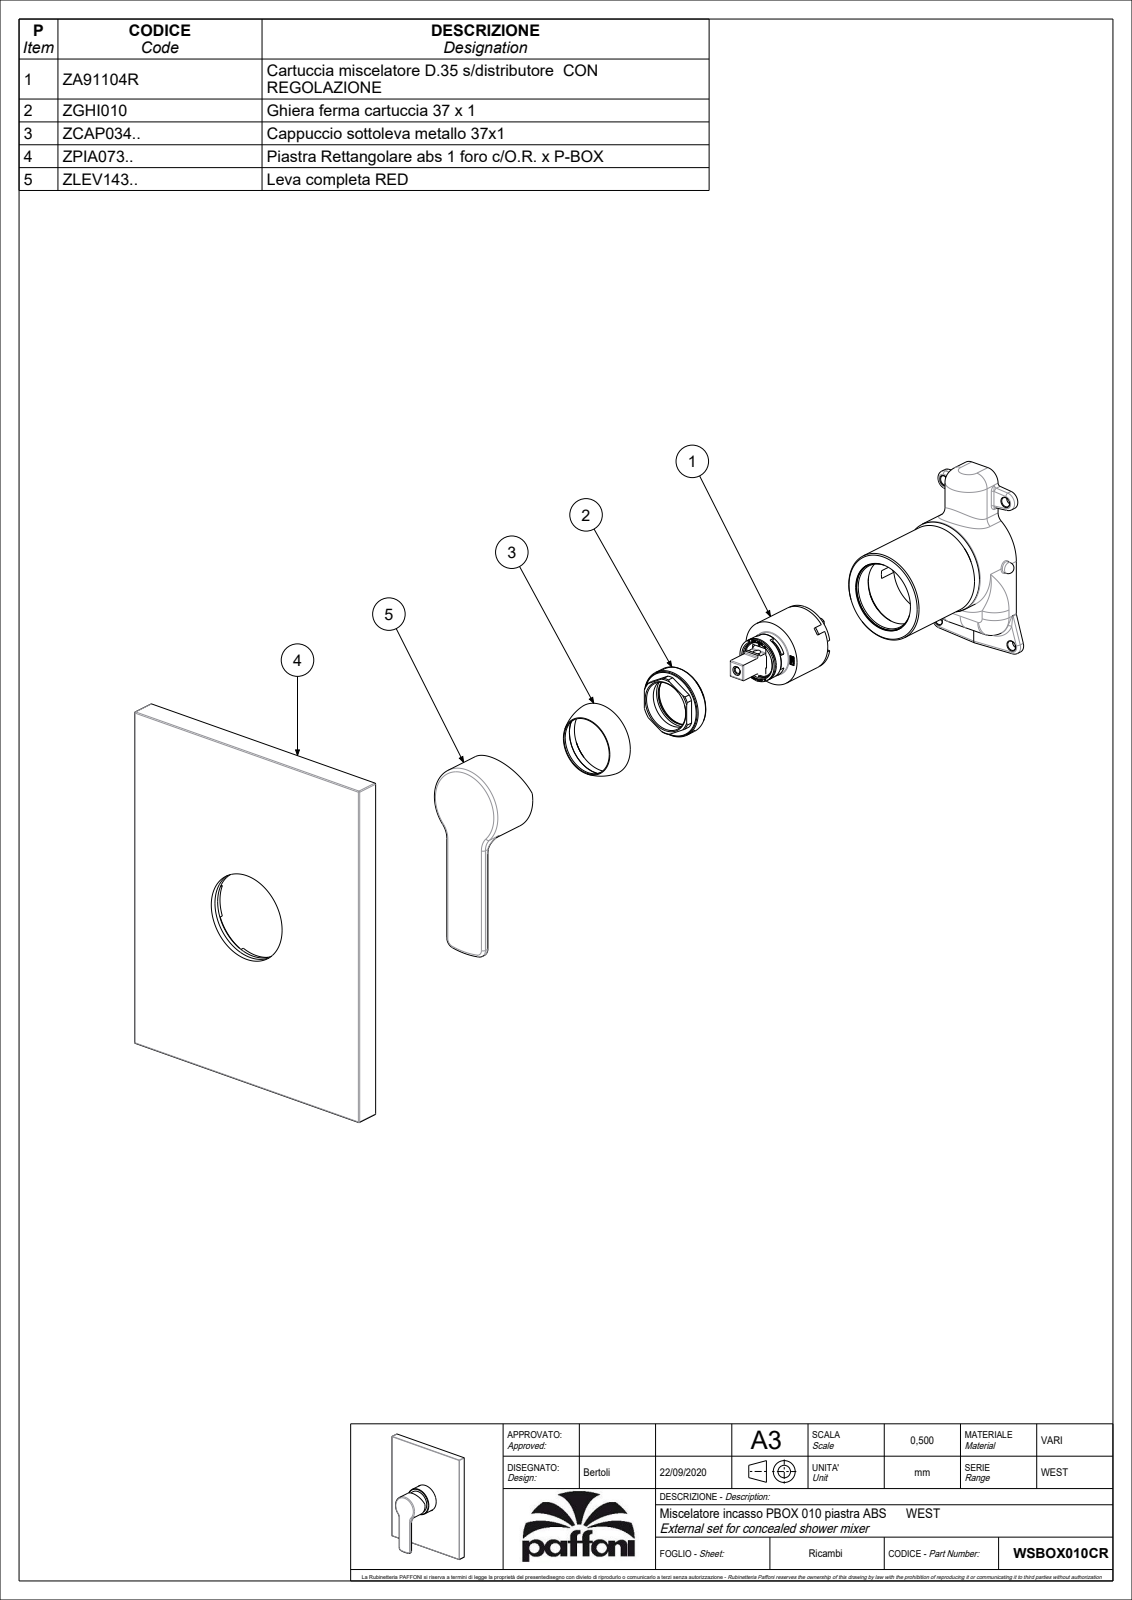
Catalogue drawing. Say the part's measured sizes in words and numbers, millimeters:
The part is named "WSBOX010CR". Its 3-D file was written by "CREO PARAMETRIC BY PTC INC, 2020044 (CONFIG_CONTROL_DESIGN)". It is 2 solids with 1135 faces: 638 planar, 295 cylindrical and 202 other. Overall it measures 192 by 154 by 70.6 millimeters. Its volume is 301 264 cubic millimeters and its surface area 120 203 square millimeters. Round holes: 3 of diameter 5, 3 of diameter 7, 2 of diameter 2, 2 of diameter 4, 1 of diameter 3, 1 of diameter 3.3, 1 of diameter 4.5, 1 of diameter 19.5, 1 of diameter 19.9, 1 of diameter 26.8, 1 of diameter 29, 1 of diameter 31. Round bosses or shafts: 2 of diameter 4.8, 1 of diameter 57, 1 of diameter 48.1, 1 of diameter 43, 1 of diameter 39, 1 of diameter 35, 1 of diameter 34.8, 1 of diameter 32.2. Partial cylindrical surfaces (rounded edges, fillets, slot ends): 74 of radius 0.5, 11 of radius 0.15, 4 of radius 0.3, 4 of radius 1.5, 2 of radius 1, 2 of radius 5, 2 of radius 10, 1 of radius 2.5. The main face-to-face distances are 13.5, 3, 10.5, 23.5, 130.5, 70.6, 60.1, 57.1, 154, 168.5. The hole center spacings are 8.6, 13.45, 15.13, 21.93, 12.5, 14, 18.
